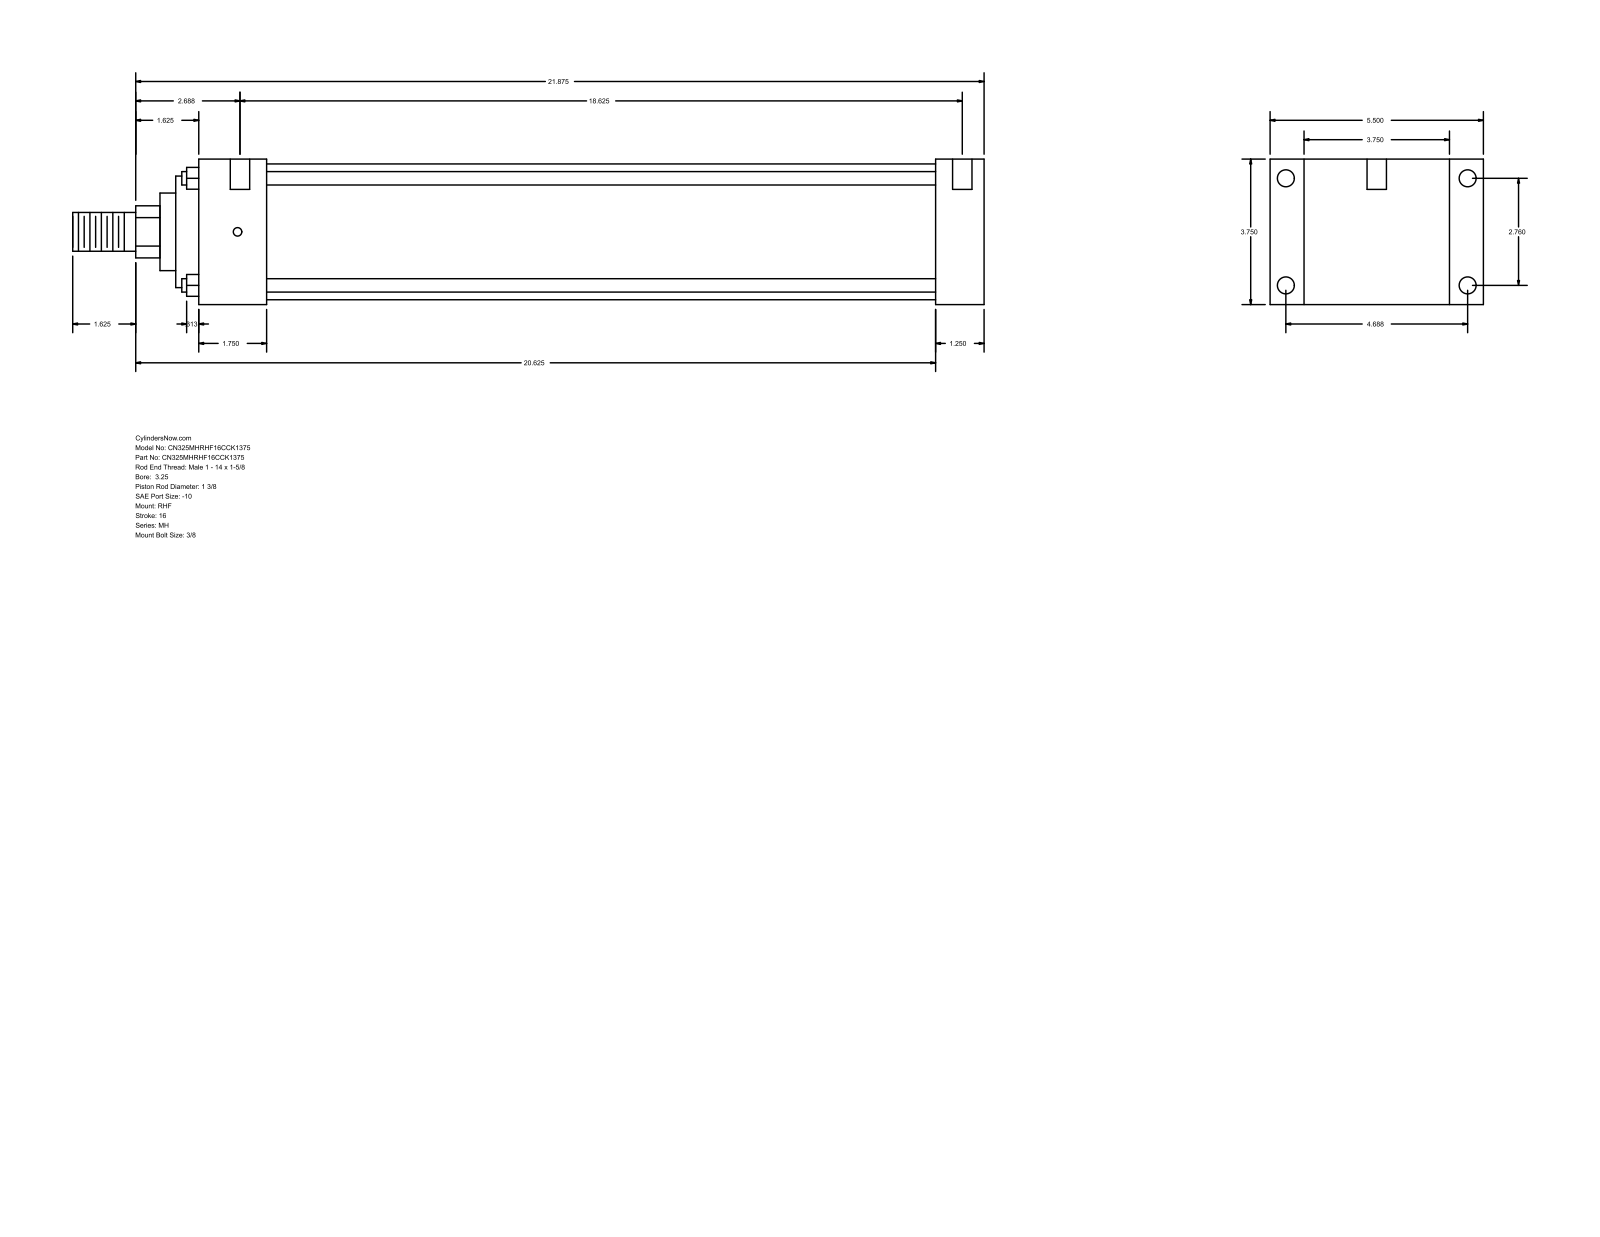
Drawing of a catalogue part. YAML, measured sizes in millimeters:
part_name: "MH_RHF__0325_1.375"
step_written_by: "GSSL Pune (CONFIG_CONTROL_DESIGN)"
units: millimeters
bodies: {solids: 0, faces: 90, planar: 61, cylindrical: 29, other: 0}
overall_size: [596.9, 139.7, 95.25]
round_holes:
  - {diameter: 5.56, count: 4}
  - {diameter: 11.13, count: 4}
  - {diameter: 12.7, count: 2}
round_bosses_or_shafts:
  - {diameter: 8.76, count: 4}
  - {diameter: 88.9, count: 1}
  - {diameter: 73.03, count: 1}
  - {diameter: 50.8, count: 1}
  - {diameter: 34.92, count: 1}
  - {diameter: 25.4, count: 1}
partial_cylinders:
  - {radius: 17.06, count: 1}
face_to_face_distances: [95.24, 31.74, 22.23, 117.47, 482.61, 514.35, 139.7, 44.45, 438.16, 469.9]
hole_center_spacings: [70.1, 119.06, 138.16, 479.43, 1.59, 4.76, 473.08, 474.67]
